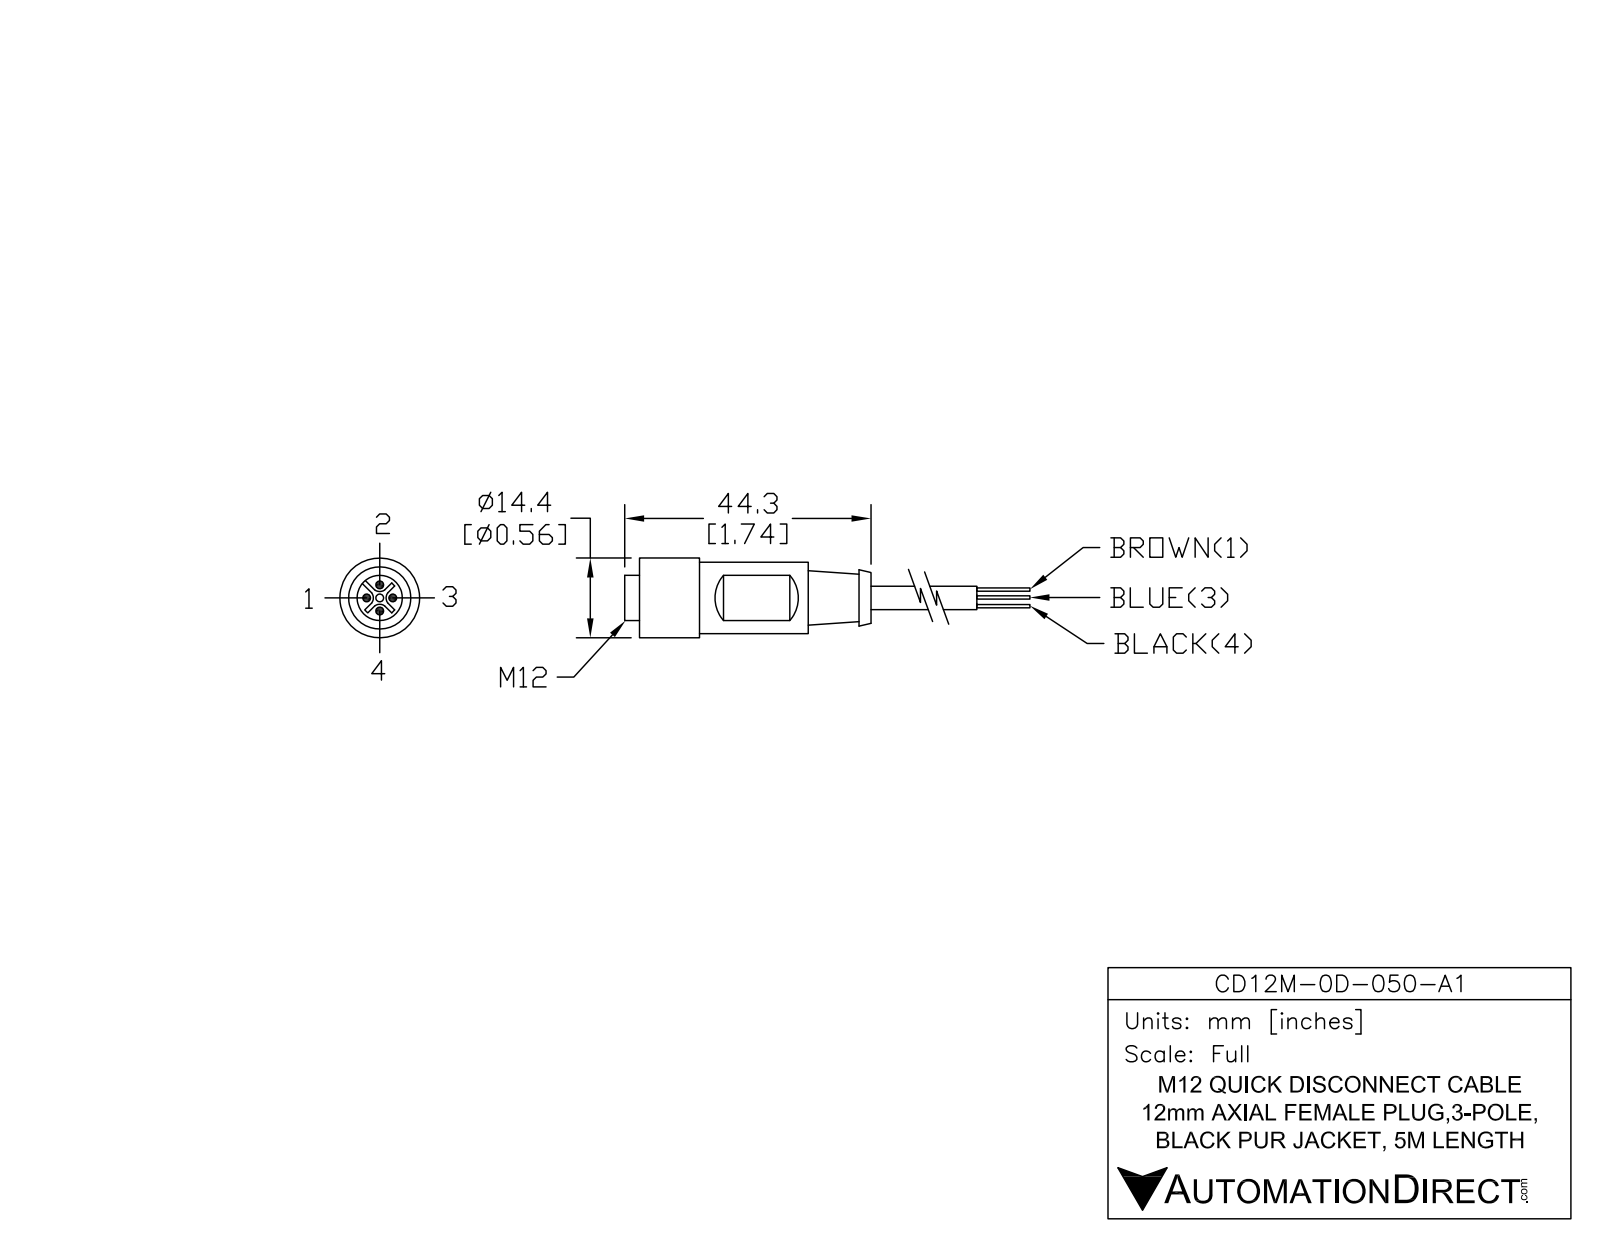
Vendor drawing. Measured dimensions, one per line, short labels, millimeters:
name: CD12M-0D-050-A1
written by: SolidWorks 2017 (AUTOMOTIVE_DESIGN)
unit: mm
bodies: 4 solids, 308 faces (195 planar, 107 cylindrical, 6 other)
size: 138.9 × 15 × 15
volume: 5 509 mm³; area: 4 482 mm²
holes: 5× ⌀1, 1× ⌀8.5, 1× ⌀12
bosses: 1× ⌀12.2, 1× ⌀10.7, 1× ⌀10.4, 1× ⌀8.9, 1× ⌀8.1, 1× ⌀4.9
rounds: 1× R0.55, 1× R7.5
face distances: 25.3, 1.4, 1.7, 8.2, 26.7, 37.2, 11.9, 10.5, 6.5, 30.7
hole spacings: 2.35, 3.32, 4.7
